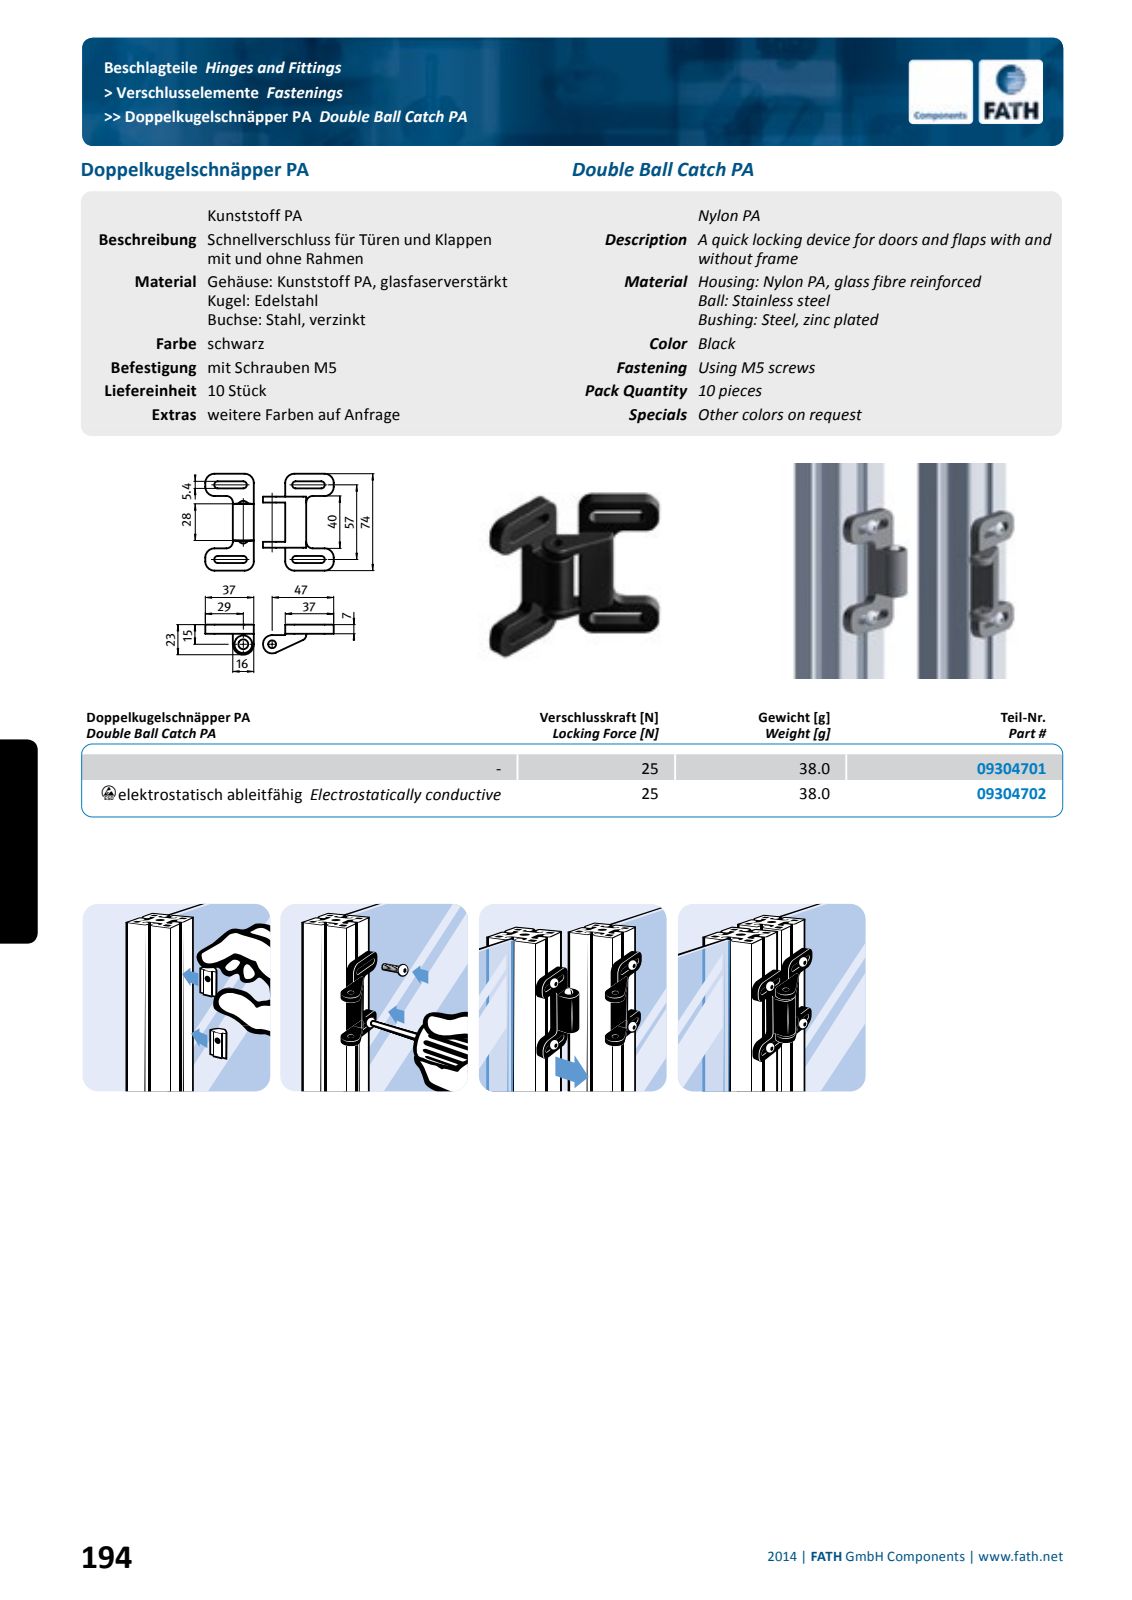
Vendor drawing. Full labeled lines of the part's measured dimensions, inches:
Part name (STEP PRODUCT): fath_09304701_1; fath_09304701_2
STEP written by: Spatial InterOp 3D (automotive_design)
Units: inches
Bodies: 2 solids, 468 faces (76 planar, 174 cylindrical, 218 other)
Overall size (bounding box): 2.992 × 2.919 × 0.9
Volume: 1.642 in³ · Surface area: 25.22 in²
Round holes (diameter × count): ⌀0.236 ×1, ⌀0.484 ×1, ⌀0.539 ×1
Partial cylindrical surfaces — rounded edges, fillets, slot ends (radius × count): R0.02 ×87, R0.039 ×24, R0.118 ×2, R0.157 ×1, R0.276 ×1, R0.31 ×1, R0.394 ×1
Main face-to-face distances: 0.276, 0.273, 0.278, 0.709, 2.242, 0.393, 0.708, 0.157, 2.244, 1.358
